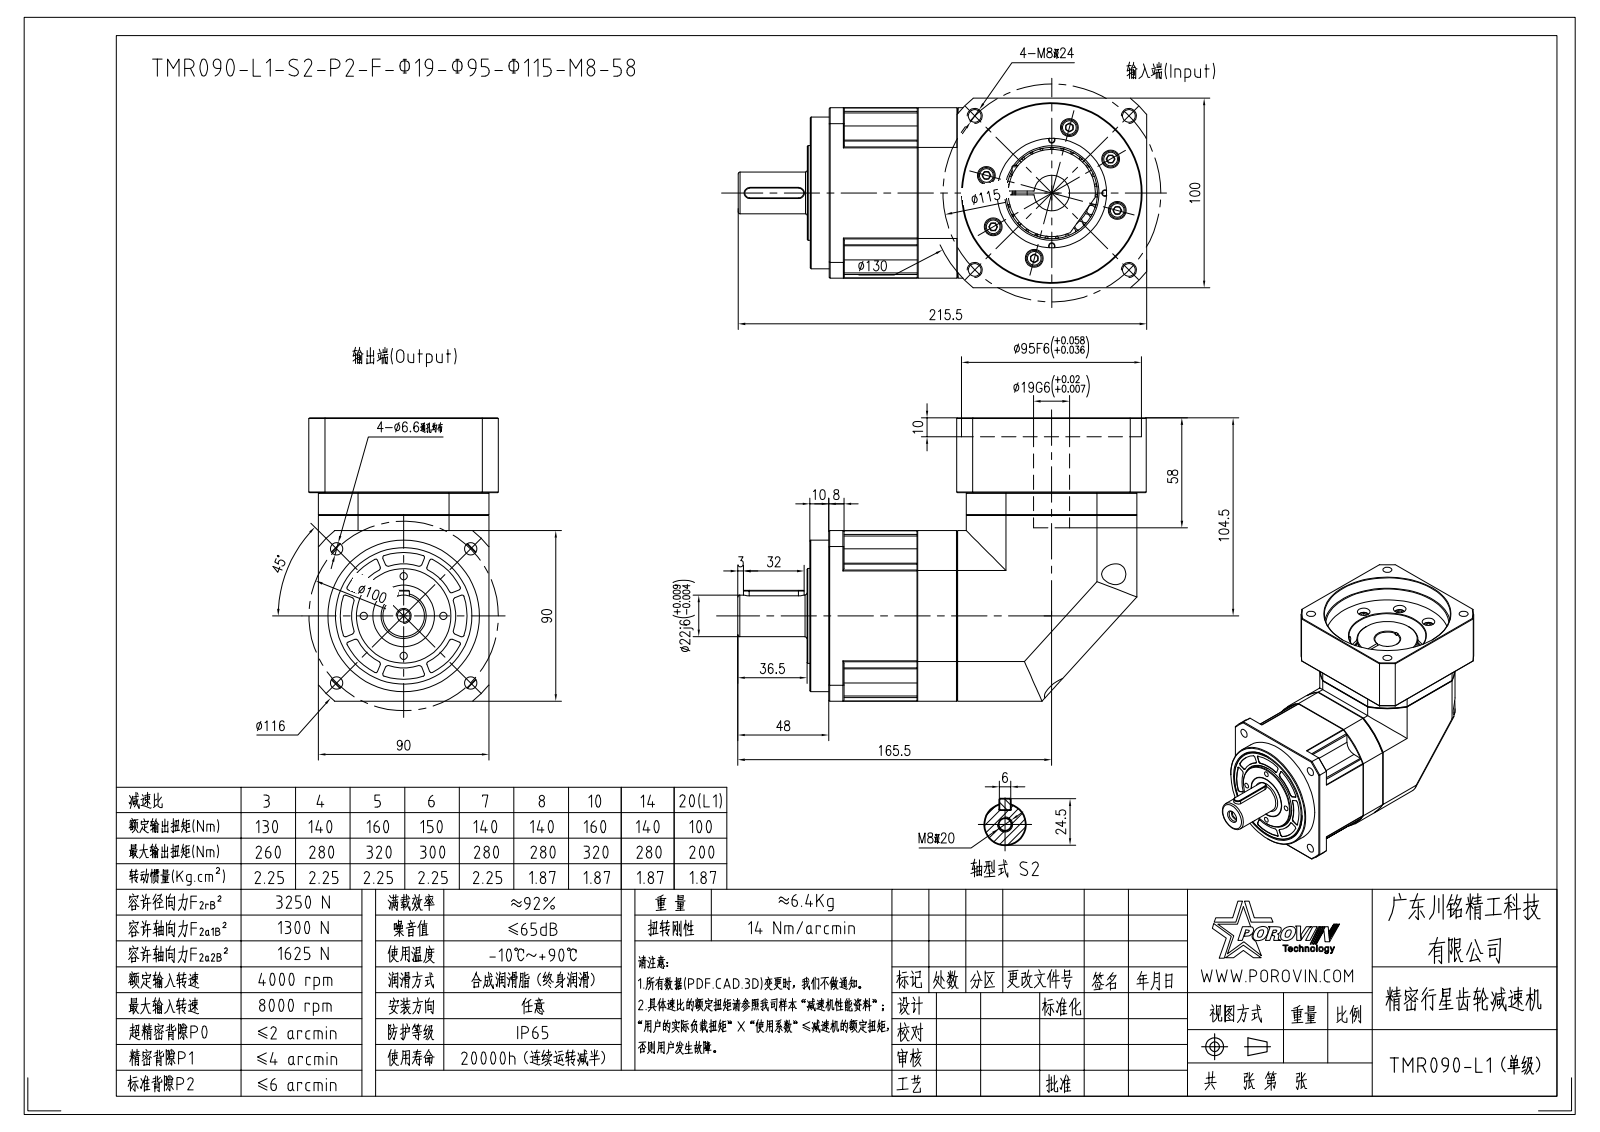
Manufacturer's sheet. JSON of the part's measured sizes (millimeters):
{"part_name": "HEXAGON_SOCKET_HEAD_CAP_S-15030; HEXAGON_SOCKET_HEAD_CAP_SC-4404; TMR900004; SPRING_LOCK_WASHERS--NORM-14923 (+8 more)", "step_written_by": "CREO PARAMETRIC BY PTC INC, 2020053 (CONFIG_CONTROL_DESIGN)", "units": "millimeters", "bodies": {"solids": 42, "faces": 1276, "planar": 513, "cylindrical": 542, "other": 221}, "overall_size": [215.5, 149.5, 100], "volume_mm3": 1403000, "surface_area_mm2": 224722, "round_holes": [[5.4, 12], [5.5, 12], [9.5, 12], [4.2, 7], [6.5, 5], [6.8, 5], [4, 4], [6.6, 4], [6.68, 4], [11, 4], [5, 1], [8.4, 1]], "round_bosses_or_shafts": [[8.5, 12], [8, 12], [5, 12], [10, 4], [9.88, 4], [6, 4], [80, 1], [78, 1]], "partial_cylinders_radius": [[1, 92], [7.5, 4], [51, 3], [3, 2], [4, 1], [5.25, 1], [40, 1], [50.25, 1]], "face_to_face_distances": [5, 90, 12, 95, 21.3, 21.5, 31.5, 20, 51.5, 10], "hole_center_spacings": [35.75, 27.36, 38.16, 66.06, 66.53, 75.16, 24.76, 59.34]}
